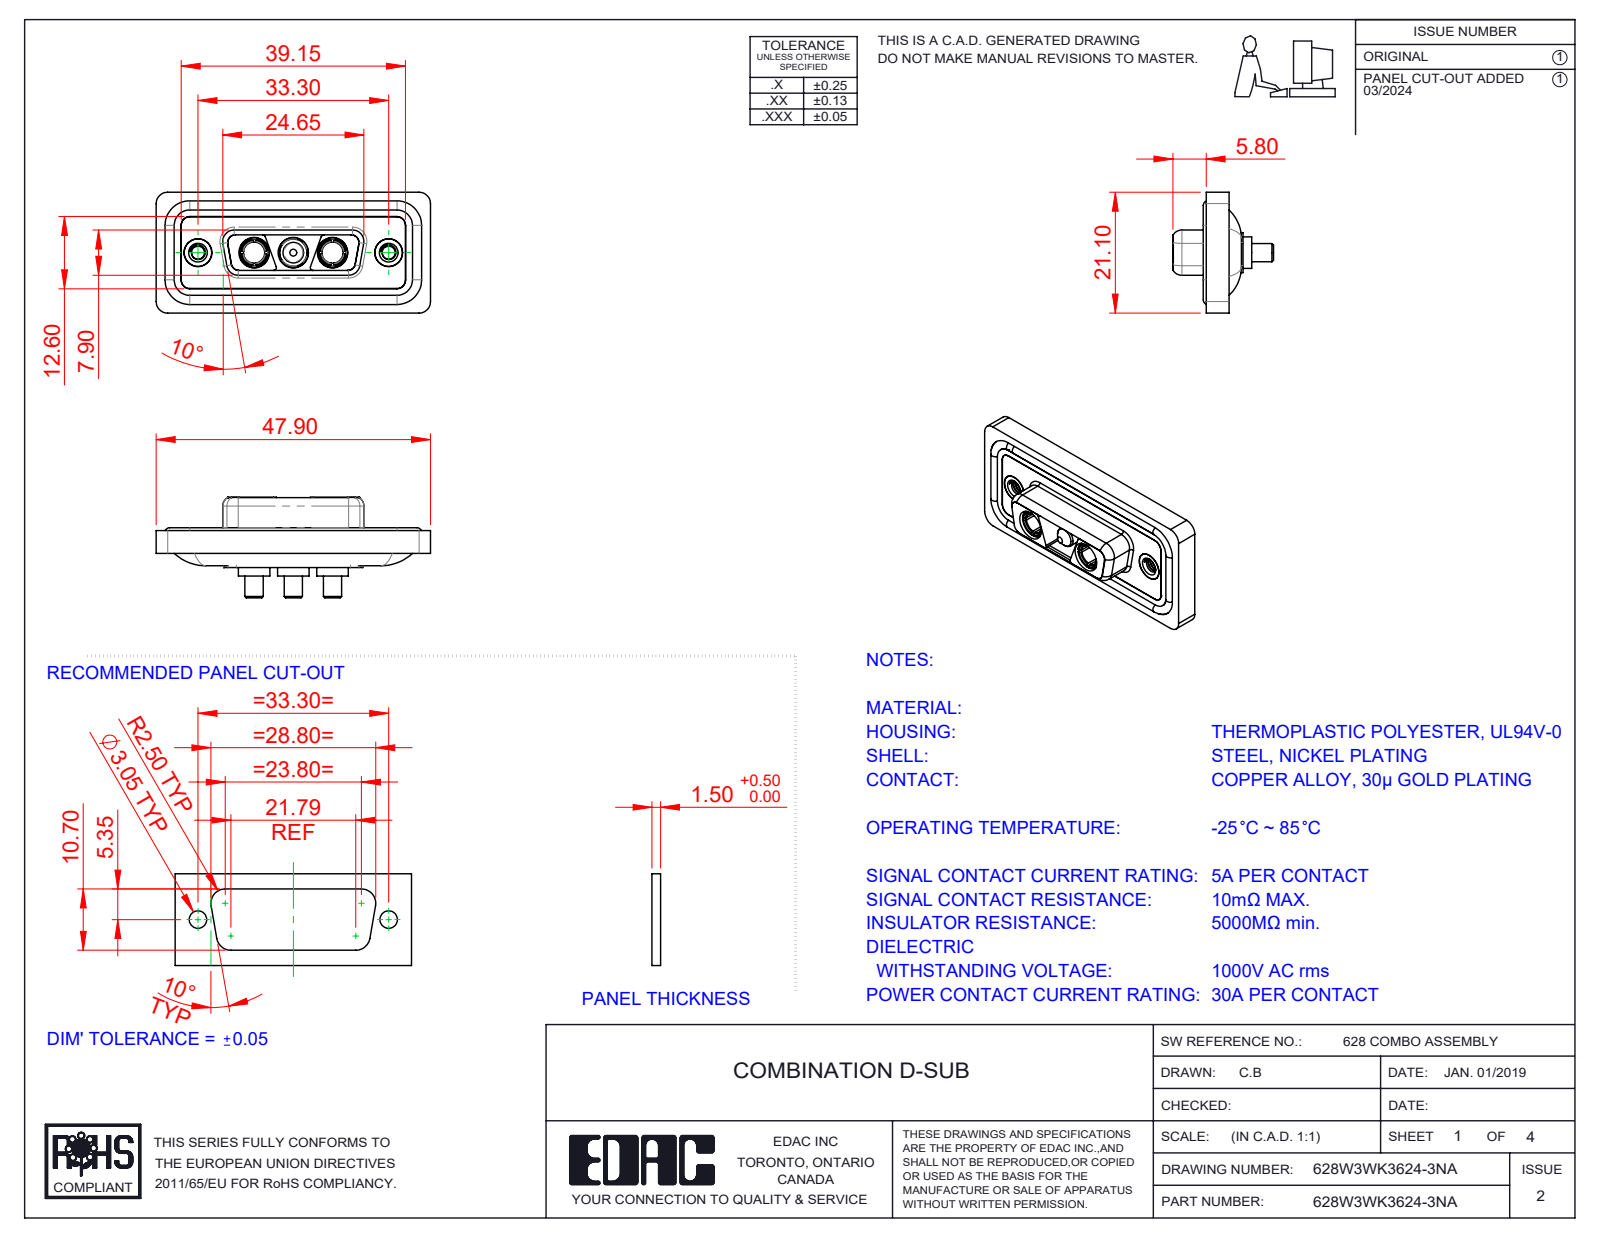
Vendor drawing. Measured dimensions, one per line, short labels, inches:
name: 628Combo Housing_3WK3; 628Combo Shell Front_15 Contacts; 628W3WK3624-3NA; Power Pin_30A S (+4 more)
written by: SolidWorks 2023 (CONFIG_CONTROL_DESIGN)
unit: in
bodies: 13 solids, 581 faces (178 planar, 260 cylindrical, 143 other)
size: 1.886 × 0.831 × 0.691
volume: 0.36 in³; area: 14.75 in²
holes: 5× ⌀0.191, 3× ⌀0.209, 2× ⌀0.089, 2× ⌀0.146, 2× ⌀0.157, 2× ⌀0.159, 2× ⌀0.197
bosses: 4× ⌀0.063, 3× ⌀0.217, 3× ⌀0.205, 3× ⌀0.187, 3× ⌀0.148, 3× ⌀0.126, 2× ⌀0.195, 2× ⌀0.195
rounds: 22× R0.059, 20× R0.079, 12× R0.053, 8× R0.02, 8× R0.063, 4× R0.01, 4× R0.024, 4× R0.026
face distances: 0.016, 0.063, 0.02, 0.071, 0.043, 0.114, 0.222, 0.278, 0.211, 0.059
hole spacings: 0.27, 0.386, 0.656, 0.925, 0.539, 1.311
